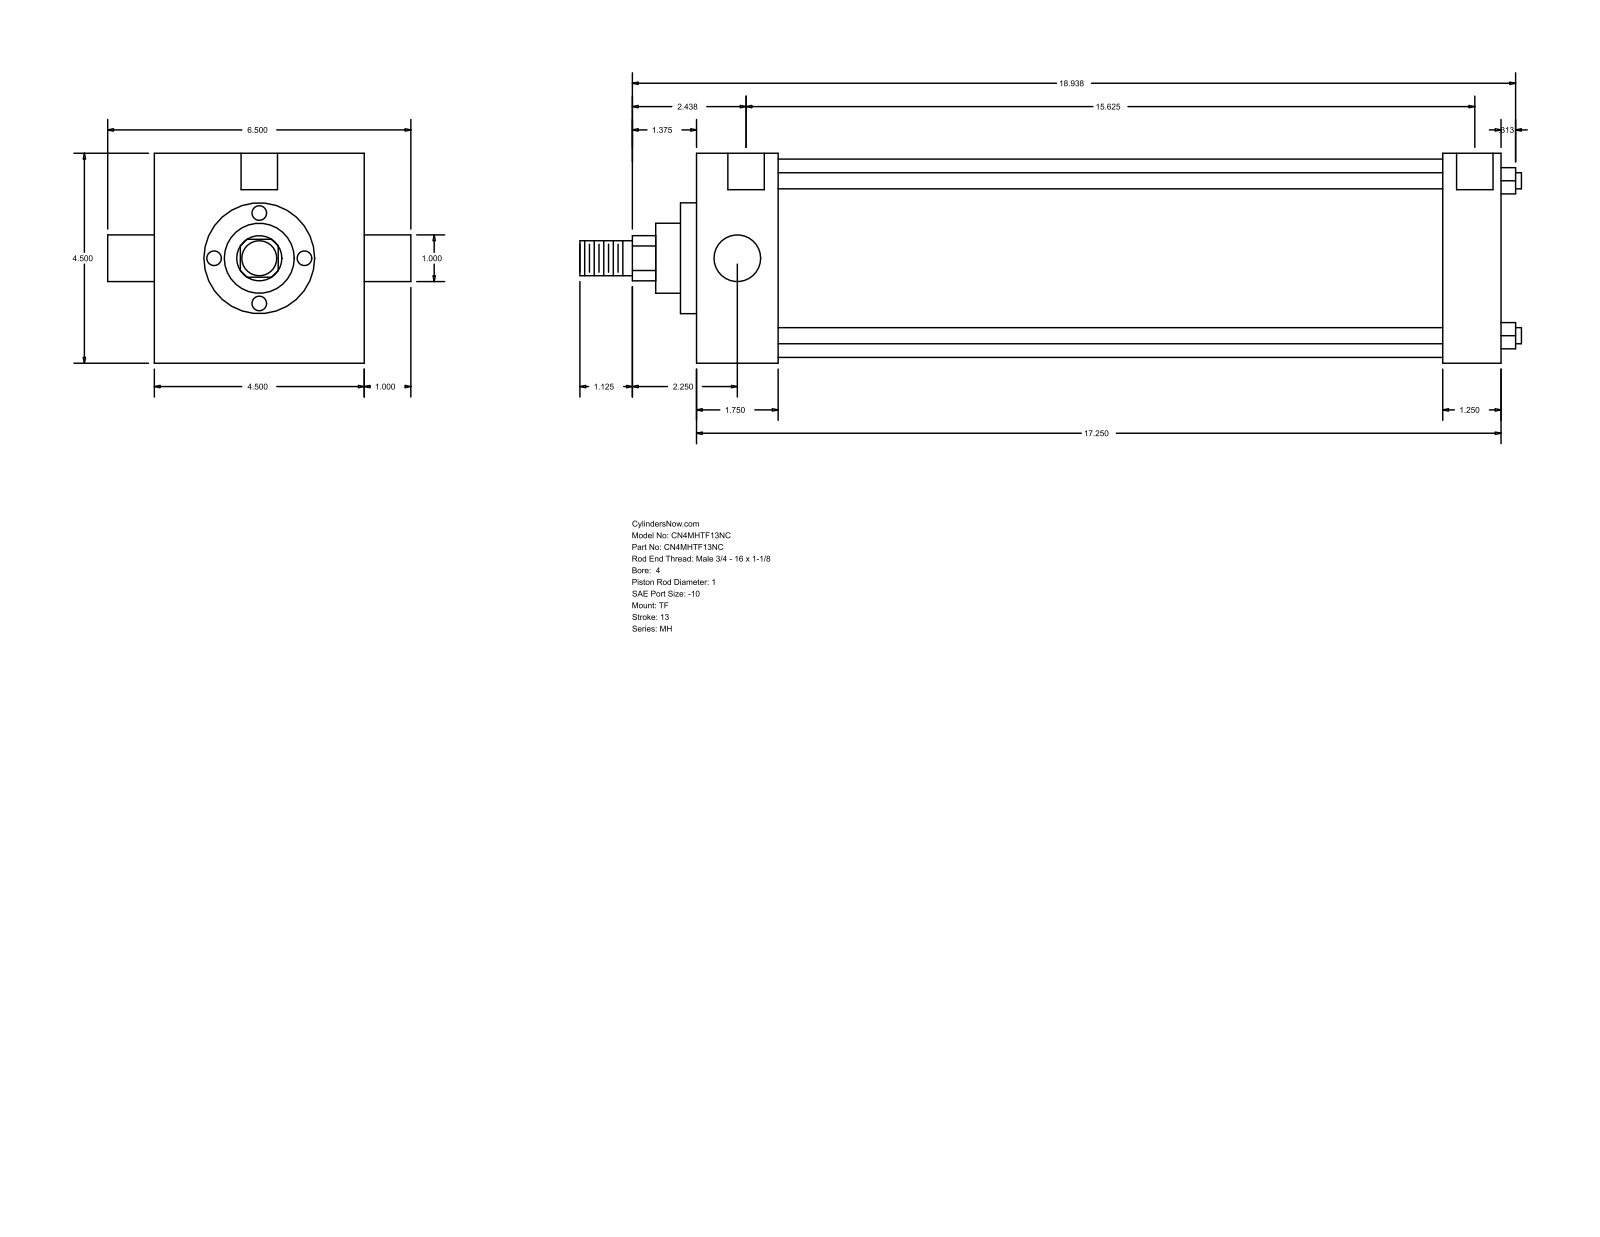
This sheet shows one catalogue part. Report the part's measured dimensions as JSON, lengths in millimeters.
{"part_name": "MH_TF__0400_1", "step_written_by": "GSSL Pune (CONFIG_CONTROL_DESIGN)", "units": "millimeters", "bodies": {"solids": 0, "faces": 86, "planar": 61, "cylindrical": 25, "other": 0}, "overall_size": [512.76, 165.1, 114.3], "round_holes": [[8.73, 3], [19.84, 2]], "round_bosses_or_shafts": [[8.76, 4], [25.4, 2], [107.95, 1], [60.33, 1], [38.1, 1], [19.05, 1]], "partial_cylinders_radius": [[12.29, 1]], "face_to_face_distances": [114.3, 438.15, 44.46, 393.69, 406.4, 361.94, 31.75, 8.73, 53.19, 415.13], "hole_center_spacings": [1.58, 1.59, 396.88, 398.46, 398.47, 400.05]}
